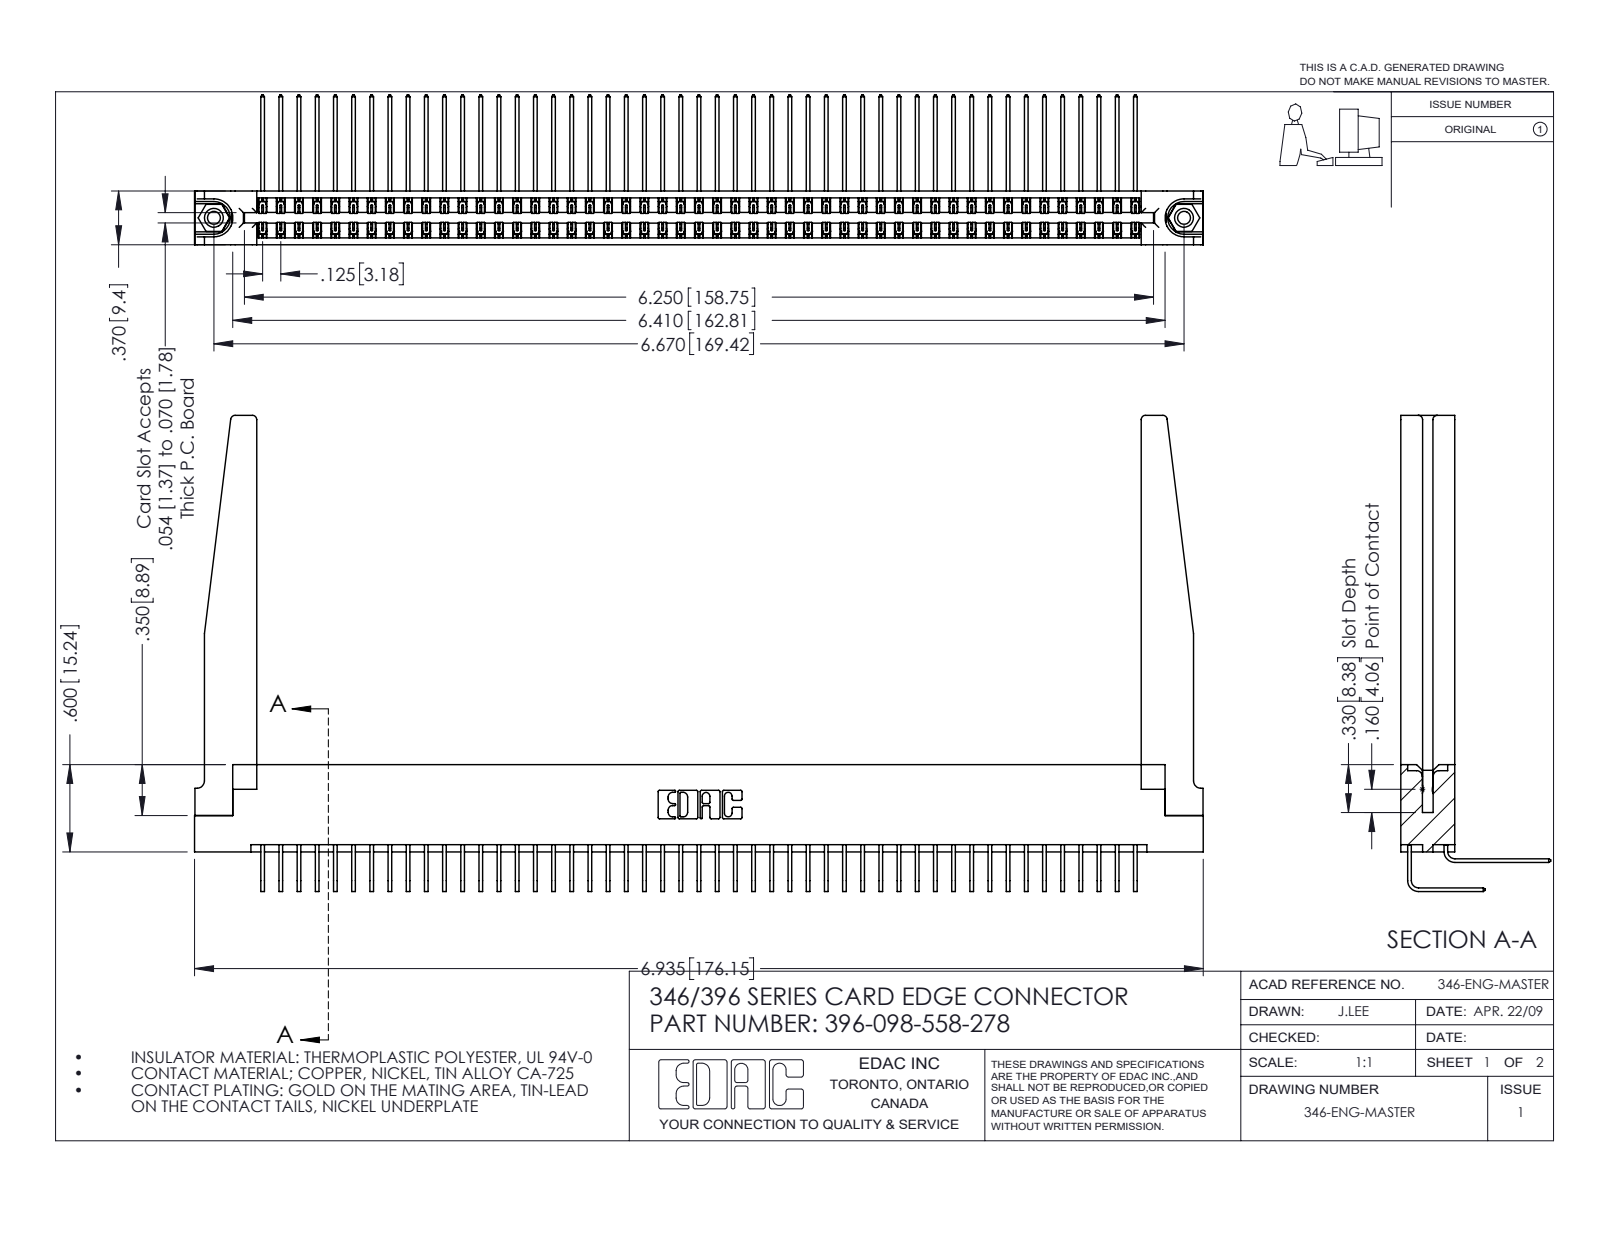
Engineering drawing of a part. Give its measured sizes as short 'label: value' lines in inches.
name: 345-292-001_558 Tail - 2; 345-250-001_345-250-001-102; 346-220-078_345-220-078; 345-292-001_558 559 Tail - 1 (+2 more)
written by: SolidWorks 2016 (CONFIG_CONTROL_DESIGN)
unit: in
bodies: 103 solids, 5648 faces (3844 planar, 1752 cylindrical, 52 other)
size: 6.935 × 3.273 × 1.03
volume: 1.508 in³; area: 52.42 in²
holes: 2× ⌀0.089, 2× ⌀0.125, 2× ⌀0.156, 1× ⌀0.064
bosses: 2× ⌀0.155
rounds: 147× R0.006, 22× R0.01, 8× R0.03, 6× R0.007, 6× R0.031, 4× R0.05, 3× R0.026, 2× R0.014
face distances: 0.322, 0.048, 0.37, 0.072, 0.025, 0.298, 0.25, 0.15, 0.148, 0.275
hole spacings: 0.246, 6.461, 6.67
